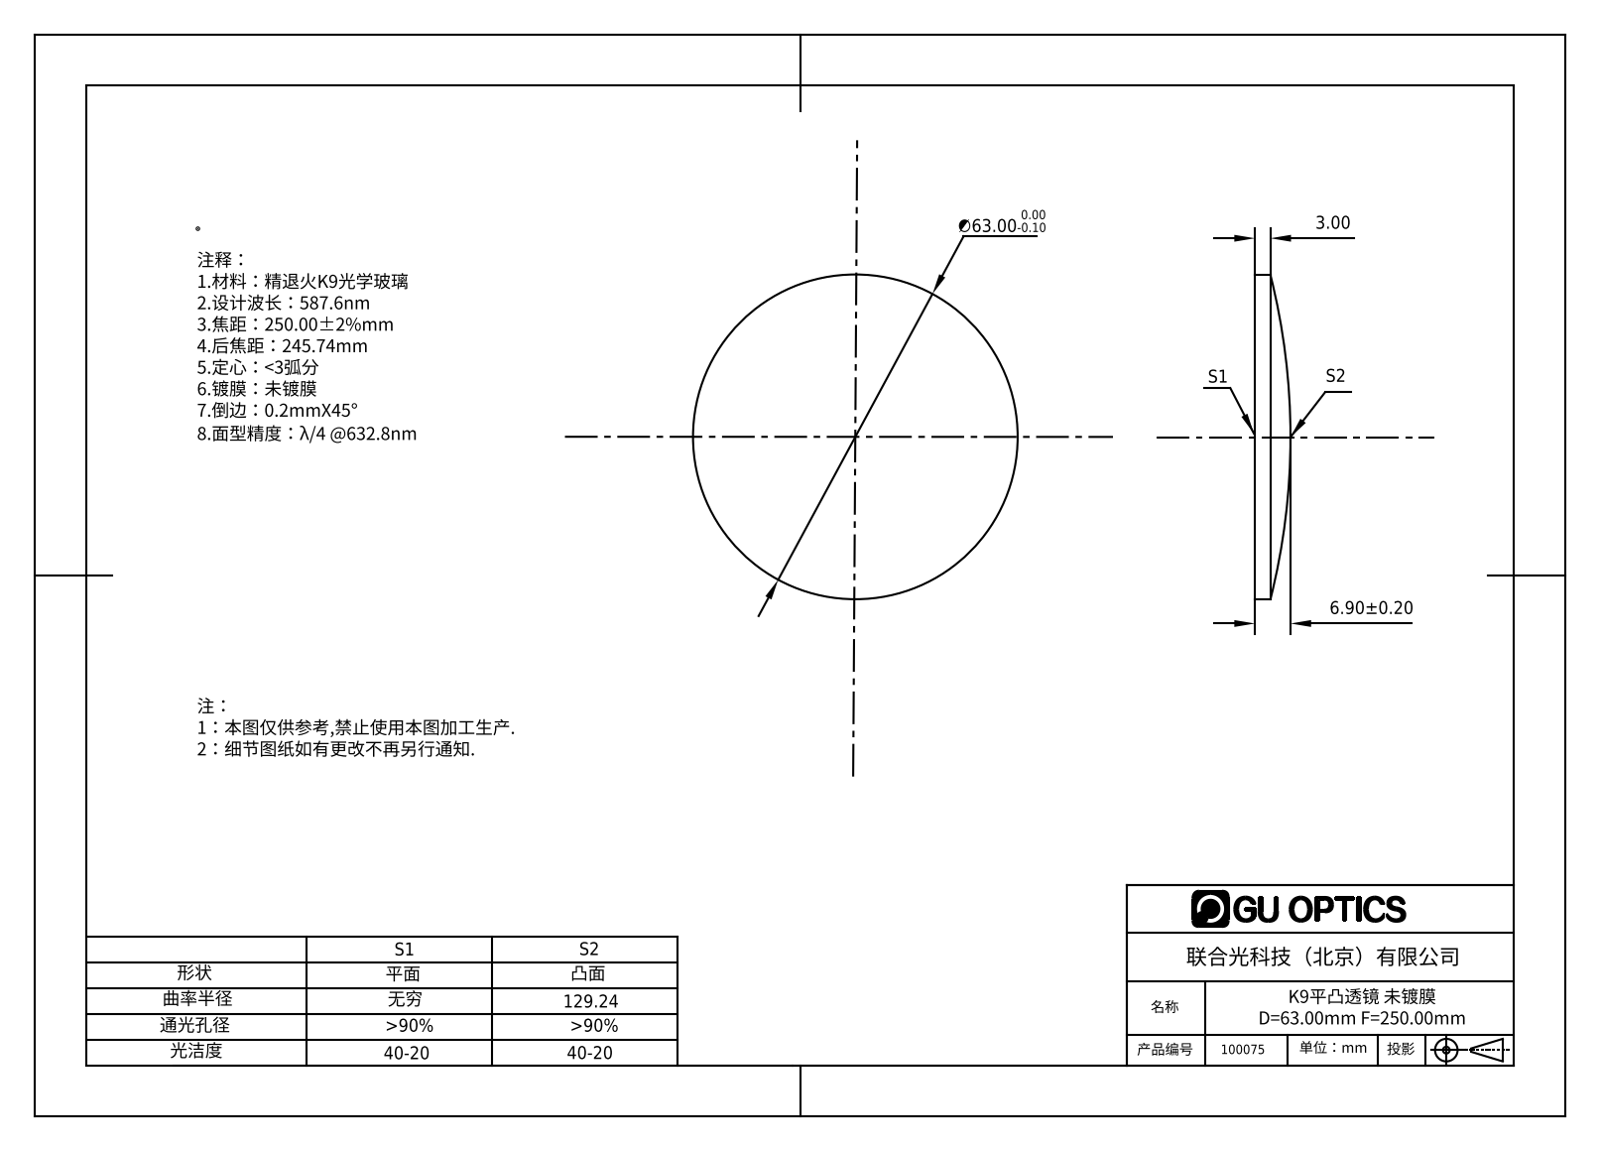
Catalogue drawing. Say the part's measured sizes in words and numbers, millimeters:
The part is named "100075". Its 3-D file was written by "SolidWorks 2016 (AUTOMOTIVE_DESIGN)". It is 1 solid with 5 faces: 1 planar, 2 cylindrical and 2 other. Overall it measures 63 by 63 by 6.9 millimeters. Its volume is 15 461 cubic millimeters and its surface area 6 876 square millimeters. Round bosses or shafts: 1 of diameter 63.
